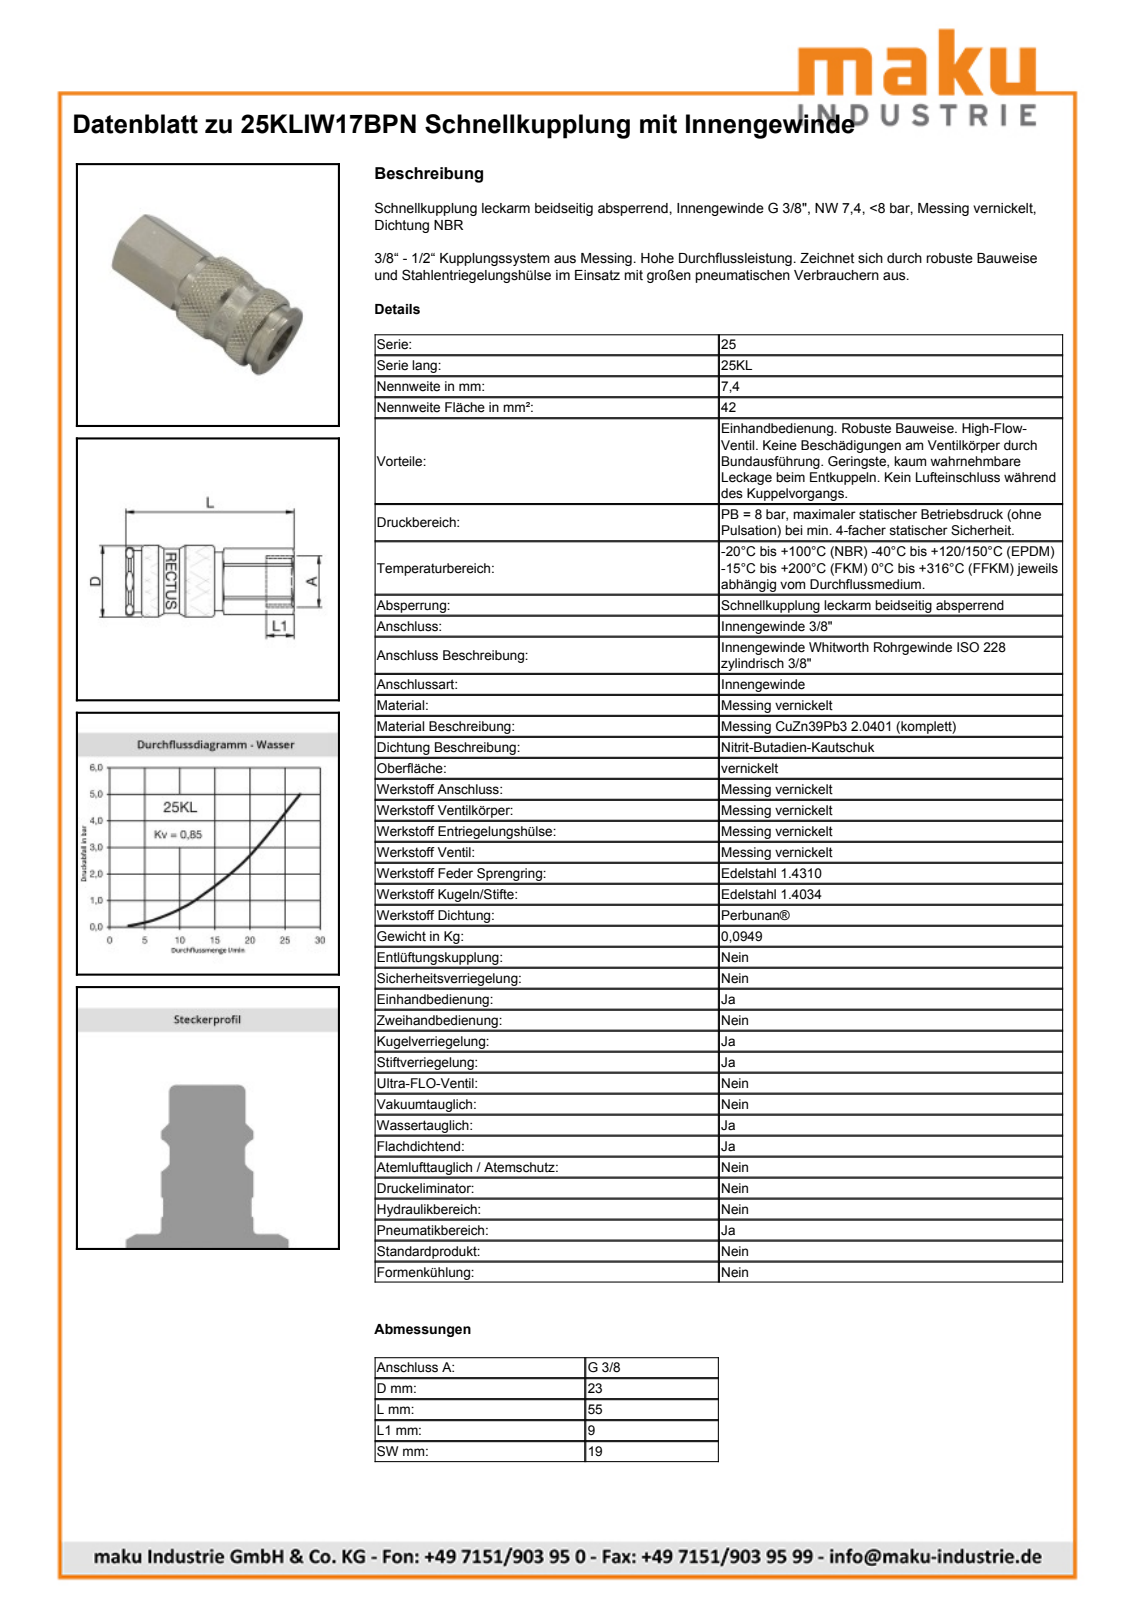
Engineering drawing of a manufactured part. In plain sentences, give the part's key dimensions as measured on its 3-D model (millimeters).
The part is named "D112169". Its 3-D file was written by "Autodesk Inventor 2013 (AUTOMOTIVE_DESIGN)". It is 2 solids with 617 faces: 210 planar, 80 cylindrical and 327 other. Overall it measures 55.1 by 23.15 by 23.15 millimeters. Its volume is 16 209 cubic millimeters and its surface area 8 277 square millimeters. Round holes: 1 of diameter 14.95, 1 of diameter 17.25, 1 of diameter 19.35, 1 of diameter 20.05. Round bosses or shafts: 1 of diameter 23.15, 1 of diameter 21, 1 of diameter 20, 1 of diameter 18.95, 1 of diameter 16, 1 of diameter 15.3. Partial cylindrical surfaces (rounded edges, fillets, slot ends): 1 of radius 10.4, 1 of radius 10.7, 1 of radius 11. The main face-to-face distances are 19, 18.98, 46.1, 21, 25.1, 55.1, 30, 9, 28.7, 3.6.
